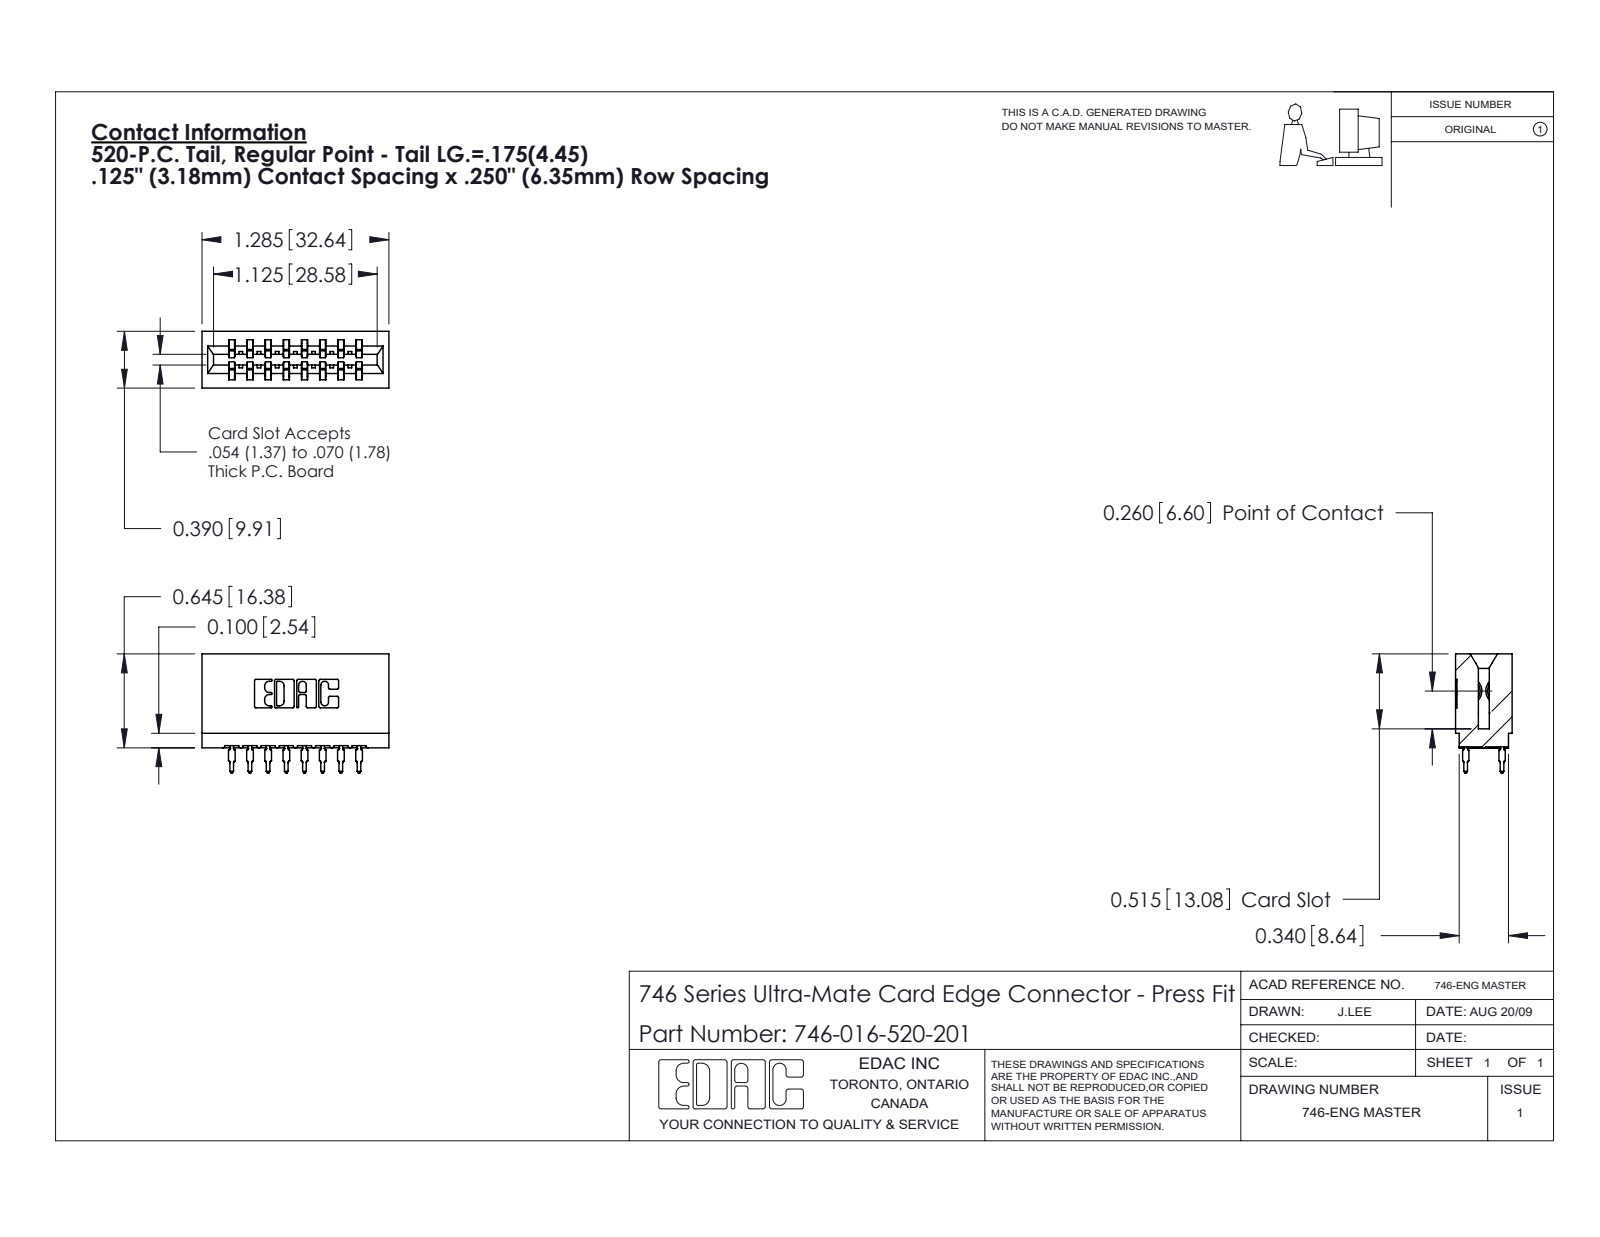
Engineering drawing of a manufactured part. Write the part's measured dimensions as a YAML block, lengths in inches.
part_name: "746 Part_.515 Slot Depth - 01; 746-016-520-201; 746-292-001_520"
step_written_by: "SolidWorks 2020 (CONFIG_CONTROL_DESIGN)"
units: inches
bodies: {solids: 17, faces: 1529, planar: 791, cylindrical: 322, other: 416}
overall_size: [1.285, 0.819, 0.39]
volume: 0.226
surface_area: 8.048
partial_cylinders:
  - {radius: 0.021, count: 32}
  - {radius: 0.01, count: 22}
  - {radius: 0.015, count: 9}
  - {radius: 0.005, count: 8}
  - {radius: 0.011, count: 8}
  - {radius: 0.007, count: 6}
  - {radius: 0.031, count: 6}
  - {radius: 0.026, count: 3}
face_to_face_distances: [0.25, 0.042, 0.125, 0.5, 0.333, 0.057, 0.292, 0.208, 0.375, 0.125]
